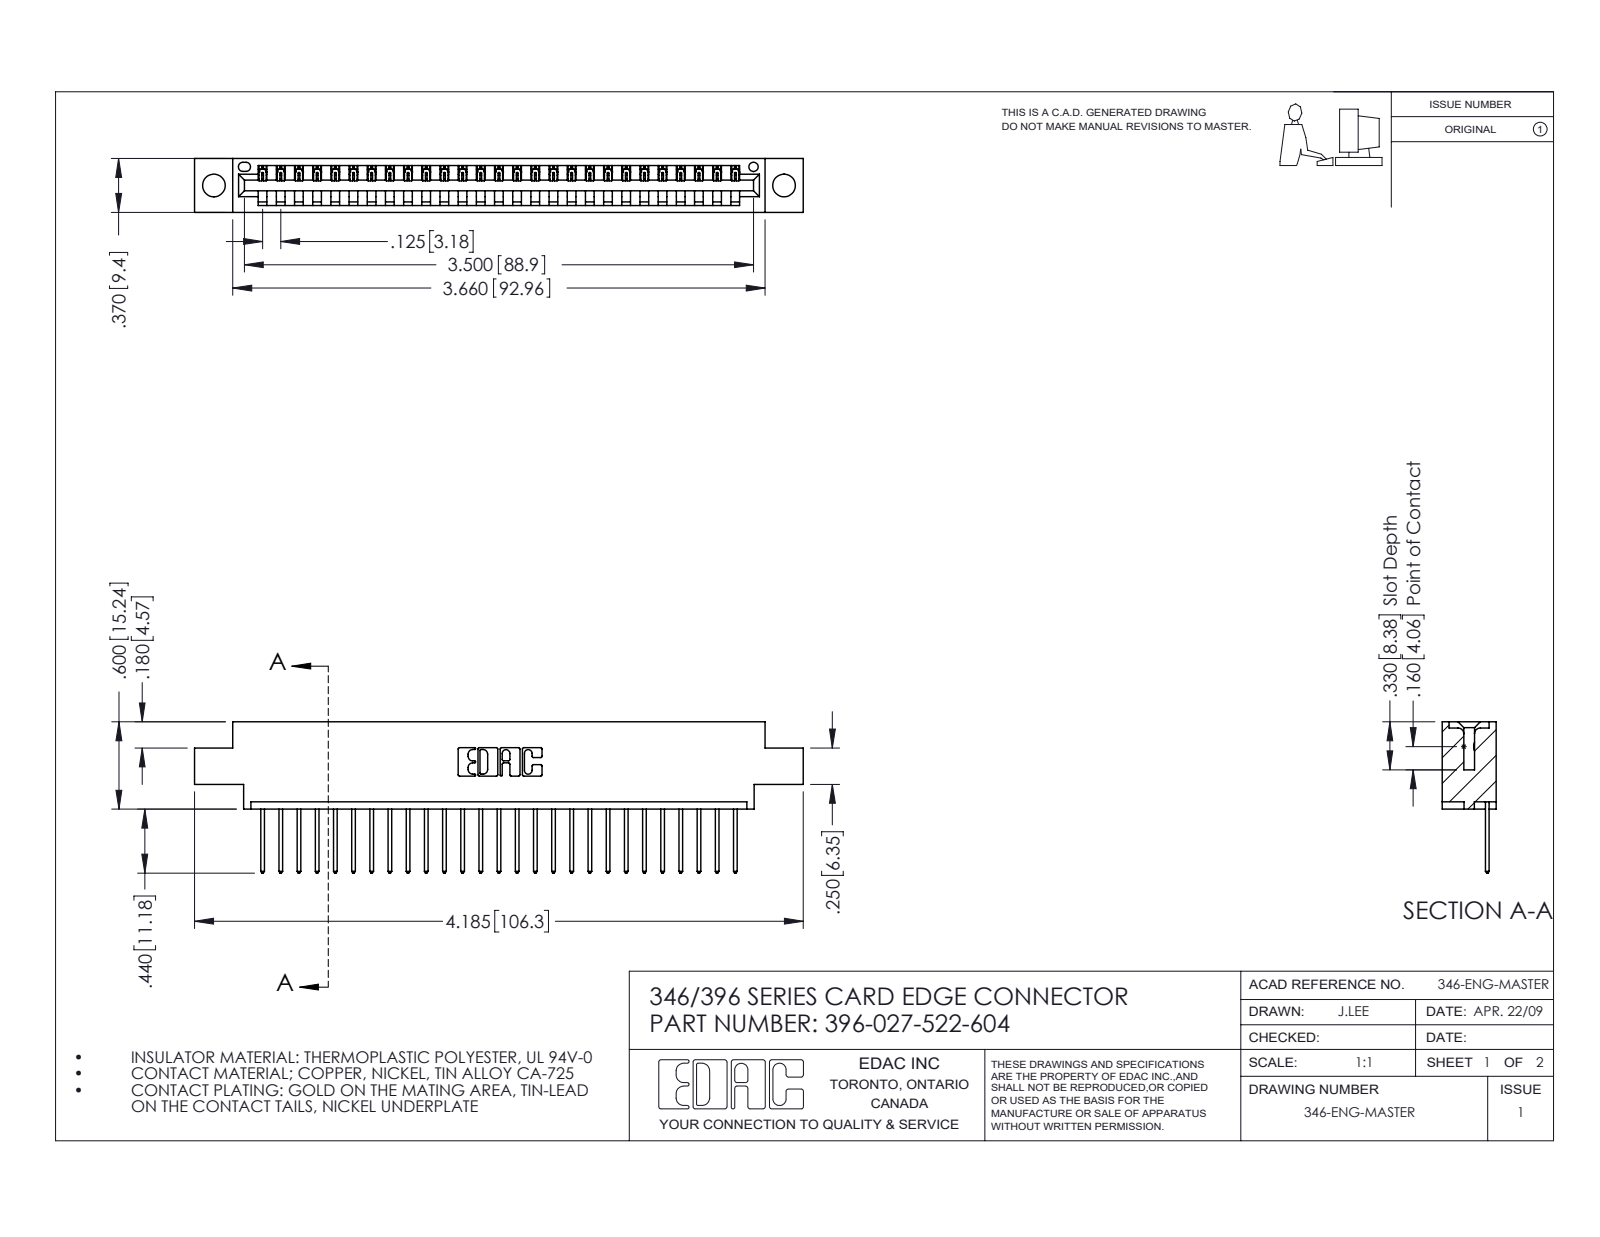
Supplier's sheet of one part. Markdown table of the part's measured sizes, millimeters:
| quantity | value |
| --- | --- |
| part name | 345-292-001_345-293-122; 396-027-522-604; 346 Part_0.170 Offset - 0.156 Dia-TH |
| STEP written by | SolidWorks 2016 (CONFIG_CONTROL_DESIGN) |
| units | millimeters |
| bodies | 28 solids, 1692 faces (1160 planar, 532 cylindrical, 0 other) |
| overall size | 106.3 × 26.4 × 9.4 |
| volume | 9 830 mm³ |
| surface area | 12 190 mm² |
| round holes (diameter × count) | 4 × 2, 1.6 × 1 |
| partial cylindrical surfaces (radius × count) | 0.2 × 54, 0.3 × 54, 0.3 × 22, 0.2 × 6, 0.8 × 6, 0.7 × 3, 0.8 × 2, 1 × 2 |
| main face-to-face distances | 1.2, 8.2, 9.4, 6.4, 1.8, 7.6, 0.6, 3.8, 5.6, 2.5 |
| hole center spacings | 6.2, 94.3, 99.6 |
